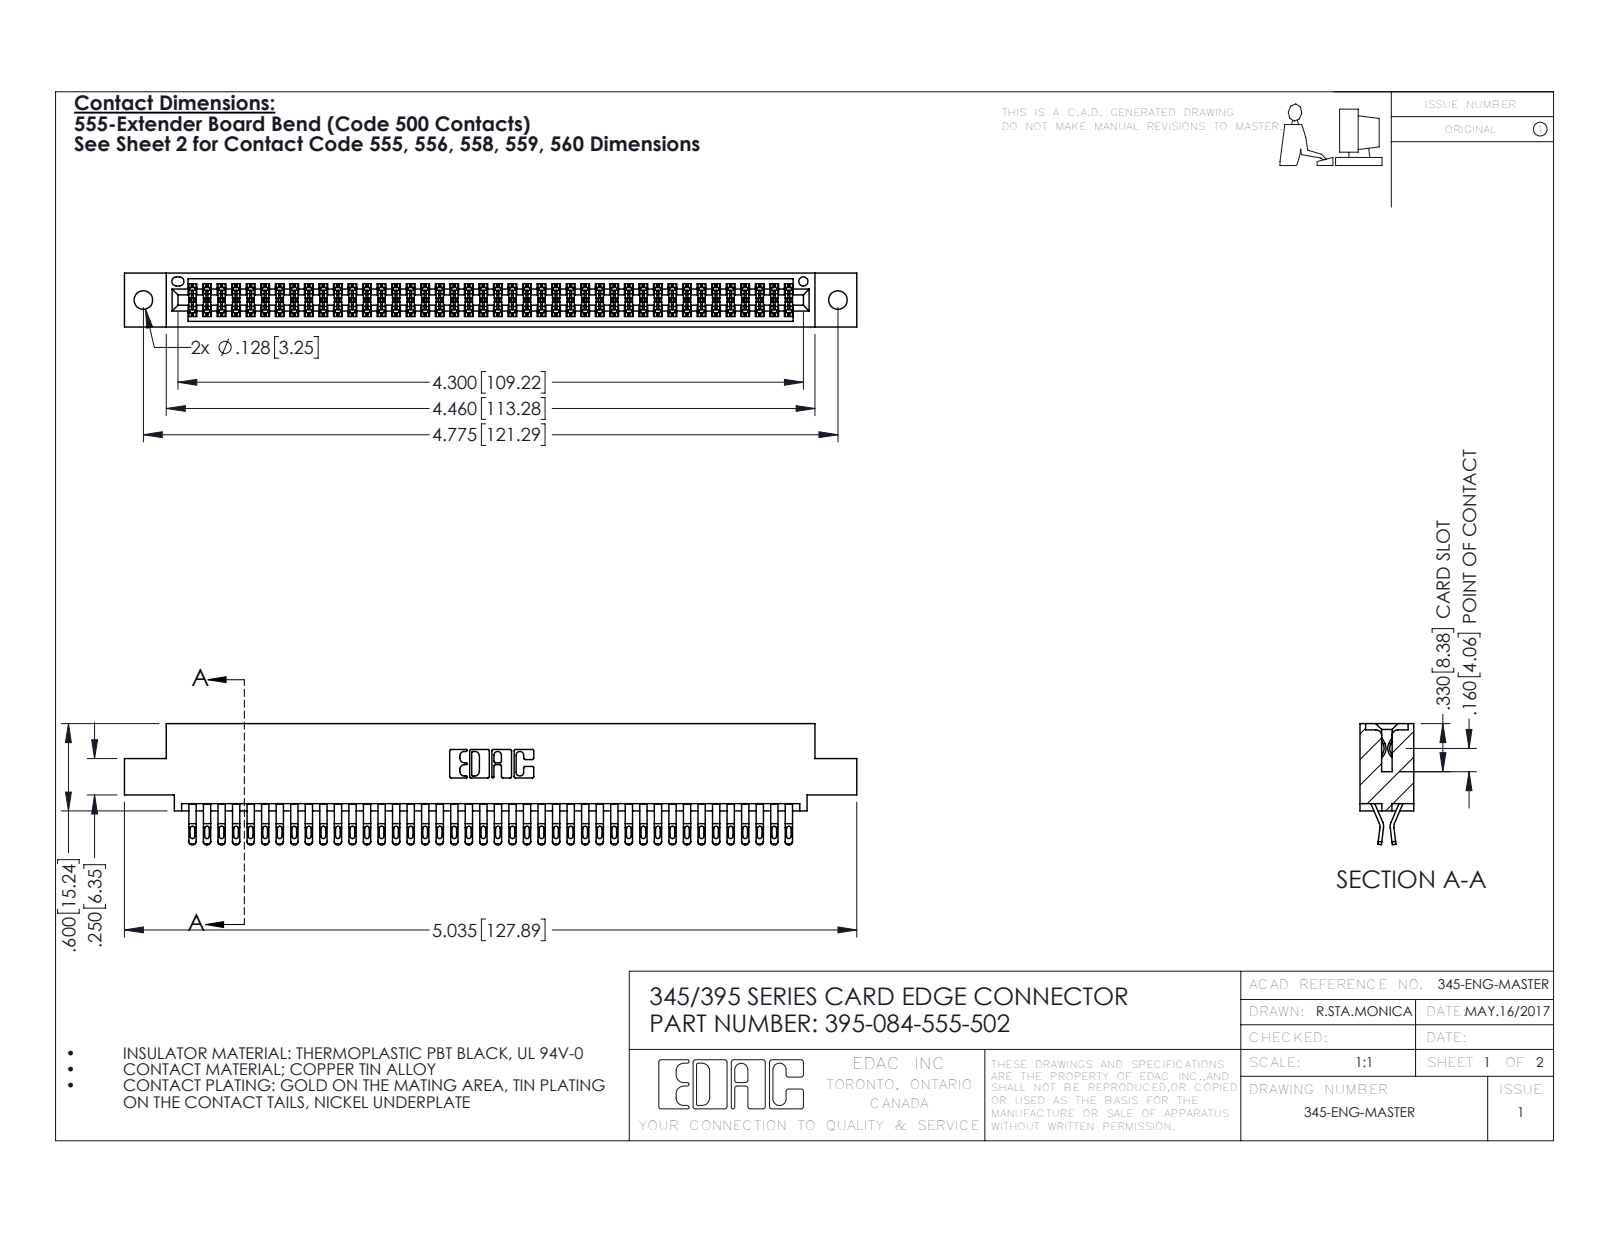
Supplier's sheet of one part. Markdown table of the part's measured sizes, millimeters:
| quantity | value |
| --- | --- |
| part name | 345 Part_0.110 Offset - 0.128 Dia; 345-292-001_555 Tail; 395-084-555-502 |
| STEP written by | SolidWorks 2016 (CONFIG_CONTROL_DESIGN) |
| units | millimeters |
| bodies | 85 solids, 4834 faces (2688 planar, 2146 cylindrical, 0 other) |
| overall size | 127.9 × 21.1 × 9.4 |
| volume | 12 600 mm³ |
| surface area | 19 230 mm² |
| round holes (diameter × count) | 3.3 × 2, 1.6 × 1 |
| partial cylindrical surfaces (radius × count) | 0.4 × 210, 0.5 × 168, 0.2 × 126, 0.3 × 22, 0.2 × 6, 0.8 × 6, 0.7 × 3, 0.3 × 2 |
| main face-to-face distances | 7.6, 1.8, 0.6, 9.4, 5.1, 2.5, 6.9, 5.7, 4.4, 3.8 |
| hole center spacings | 6.9, 115.3, 121.3 |
